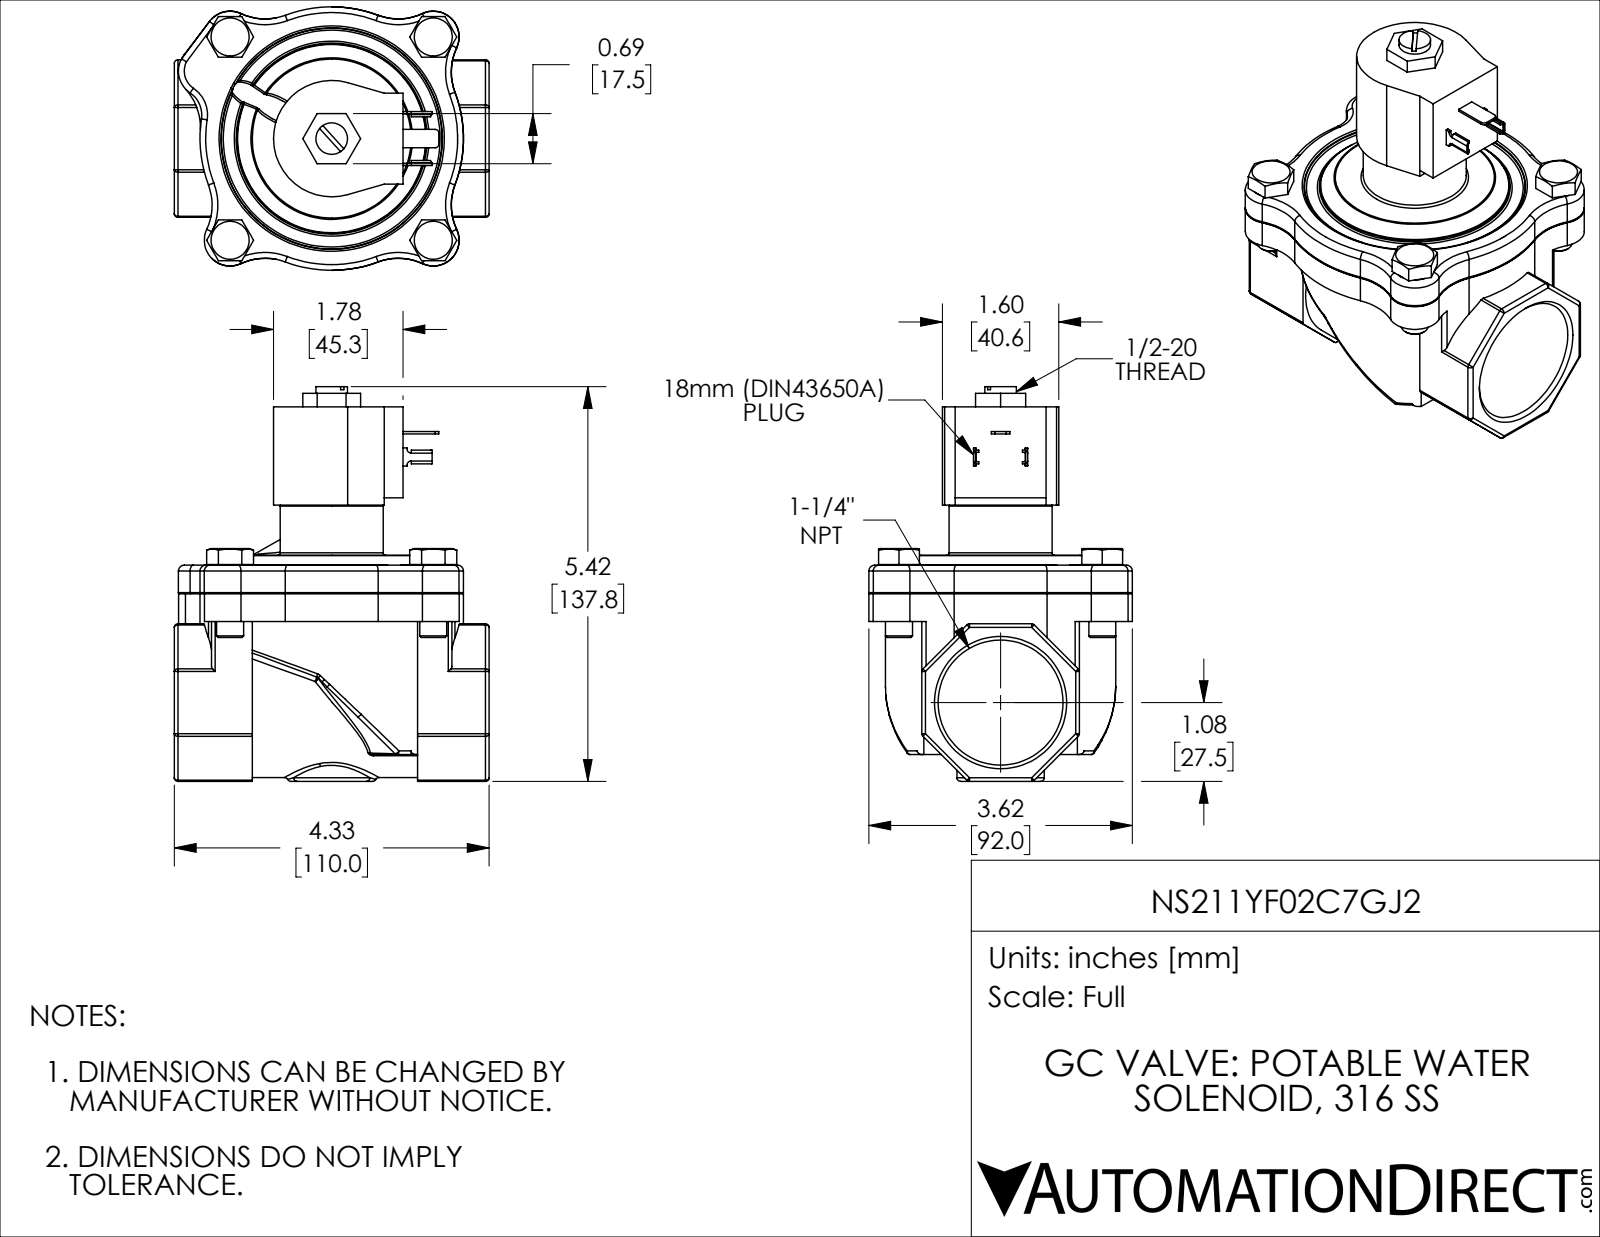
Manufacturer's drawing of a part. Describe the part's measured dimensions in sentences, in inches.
The part is named "NS211YF02C7GJ2". Its 3-D file was written by "SolidWorks 2018 (AUTOMOTIVE_DESIGN)". It is 9 solids with 503 faces: 155 planar, 161 cylindrical and 187 other. Overall it measures 5.424 by 4.33 by 3.622 inches. Its volume is 26.48 cubic inches and its surface area 135.5 square inches. Round holes: 4 of diameter 0.375, 4 of diameter 0.433, 1 of diameter 0.125, 1 of diameter 0.434, 1 of diameter 0.846, 1 of diameter 0.949, 1 of diameter 1.718. Round bosses or shafts: 4 of diameter 0.504, 4 of diameter 0.37, 1 of diameter 1.417. Partial cylindrical surfaces (rounded edges, fillets, slot ends): 32 of radius 0.05, 15 of radius 0.787, 8 of radius 0.354, 4 of radius 0.006, 4 of radius 0.041, 2 of radius 0.06, 2 of radius 0.362, 2 of radius 1.811. The main face-to-face distances are 0.393, 1.22, 0.827, 2.57, 2.177, 1.35, 2.578, 2.97, 3.798, 5.148. The hole center spacings are 2.795, 1.976, 1.977, 2.794, 2.795, 3.952, 3.953.
